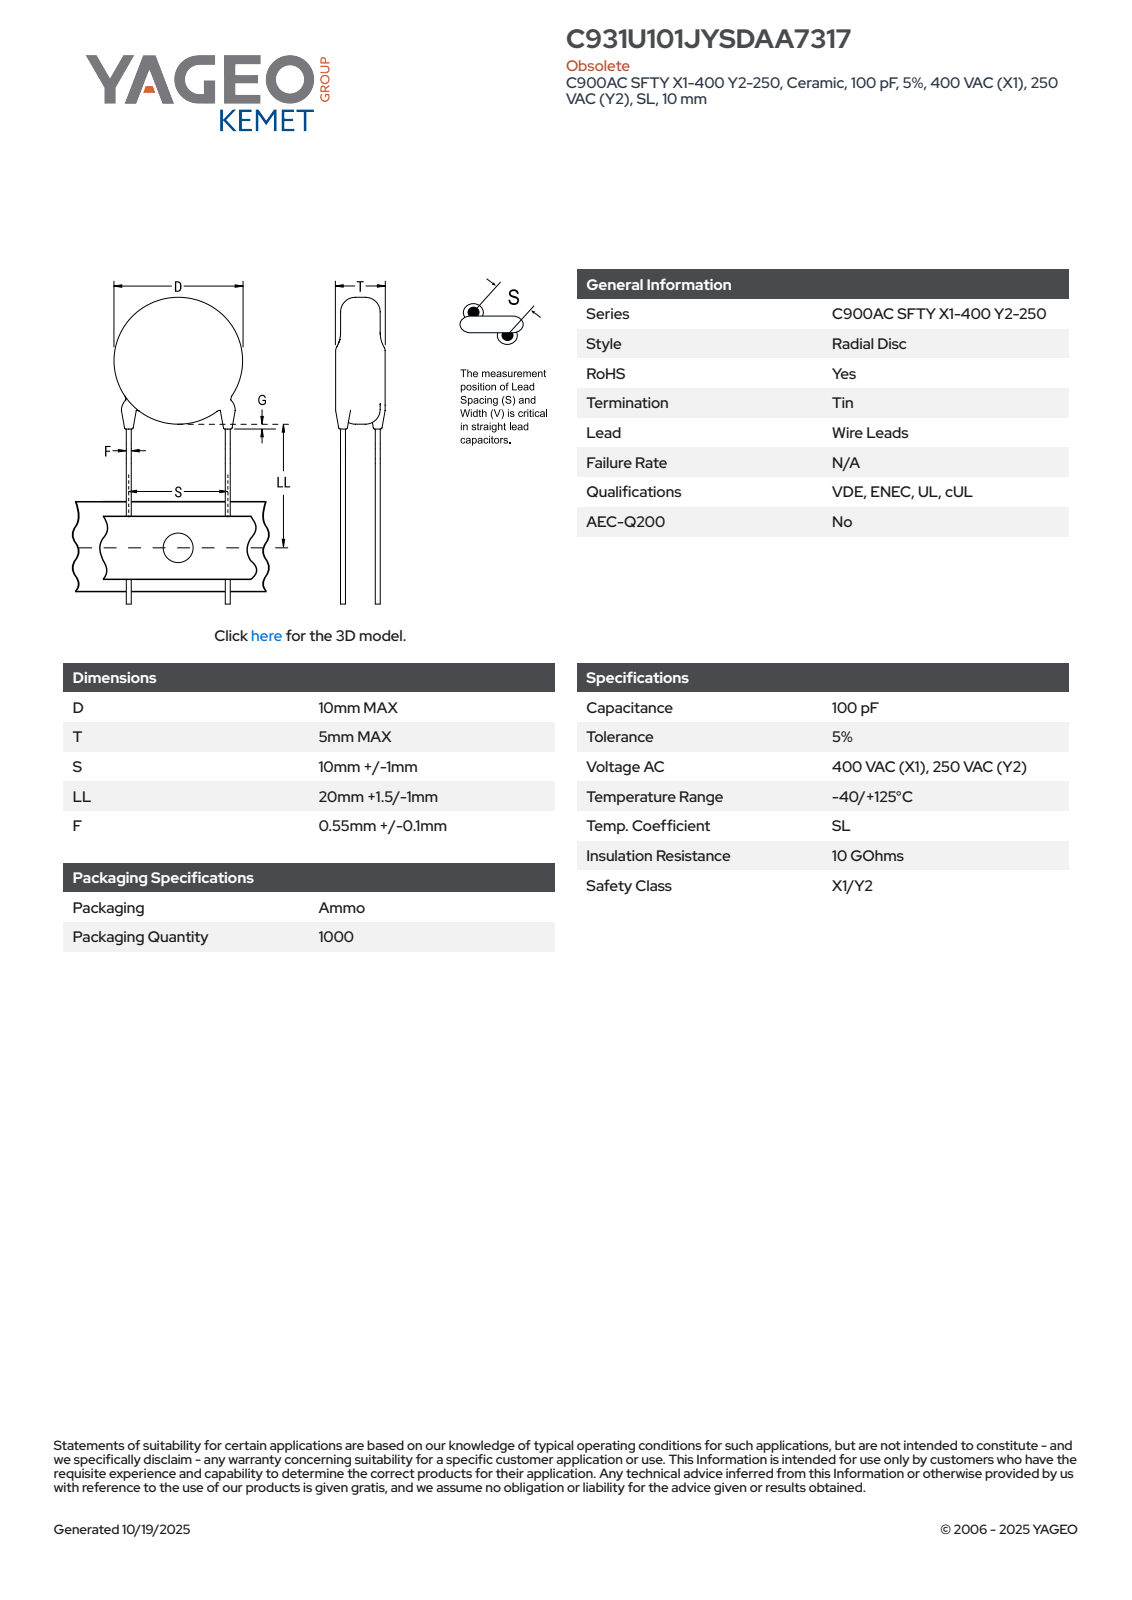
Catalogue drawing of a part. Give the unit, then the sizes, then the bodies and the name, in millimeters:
Units: millimetres
Overall size (bounding box): 31.5 × 10 × 5.09
Round bosses / shafts (diameter × count): ⌀0.65 ×2, ⌀10 ×1
Main face-to-face distances: 5, 27.07, 25.92, 1.15, 0.93, 0.42, 0.31, 3.43, 3.56, 1.89
Volume: 398 mm³ · Surface area: 393 mm²
Bodies: 4 solids, 83 faces (61 planar, 6 cylindrical, 16 other)
Part name (STEP PRODUCT): CCD_STC900_D10T5S10LL21.5F0.65G3
STEP written by: SolidWorks 2014 (AUTOMOTIVE_DESIGN)
